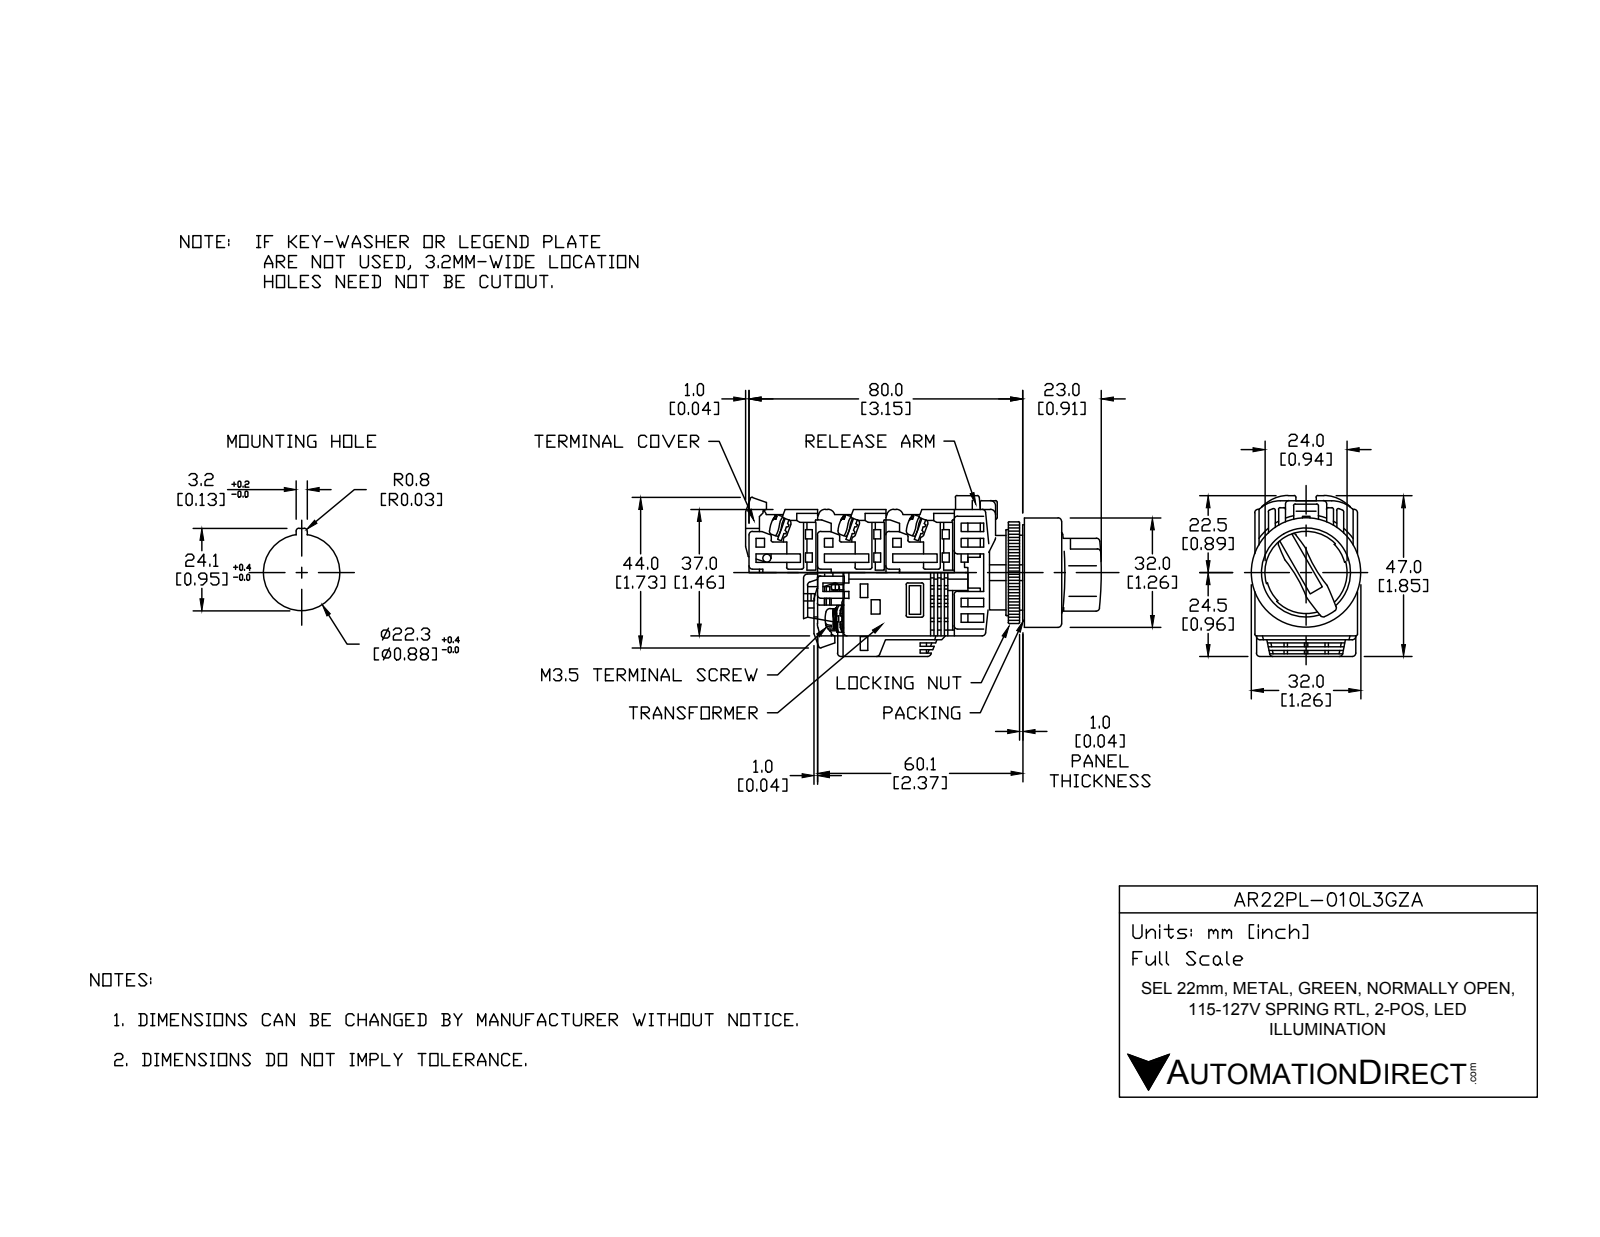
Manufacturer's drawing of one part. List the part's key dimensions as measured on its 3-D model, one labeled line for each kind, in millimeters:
Part name (STEP PRODUCT): AR22PL-010L3GZA
STEP written by: SolidWorks 2017 (AUTOMOTIVE_DESIGN)
Units: millimetres
Bodies: 18 solids, 462 faces (317 planar, 118 cylindrical, 27 other)
Overall size (bounding box): 84.5 × 43.81 × 32
Volume: 48 971 mm³ · Surface area: 26 711 mm²
Round holes (diameter × count): ⌀21.8 ×1, ⌀22 ×1, ⌀25 ×1, ⌀31 ×1
Round bosses / shafts (diameter × count): ⌀5 ×4, ⌀32 ×1, ⌀30.5 ×1, ⌀29.8 ×1, ⌀24 ×1, ⌀21.75 ×1, ⌀17 ×1
Partial cylindrical surfaces — rounded edges, fillets, slot ends (radius × count): R0.5 ×39, R1.75 ×8, R1 ×6, R5 ×4, R4 ×2, R12 ×1, R16.59 ×1, R17.59 ×1
Main face-to-face distances: 1, 18, 29, 20, 3, 28.5, 0.5, 2, 21, 10
